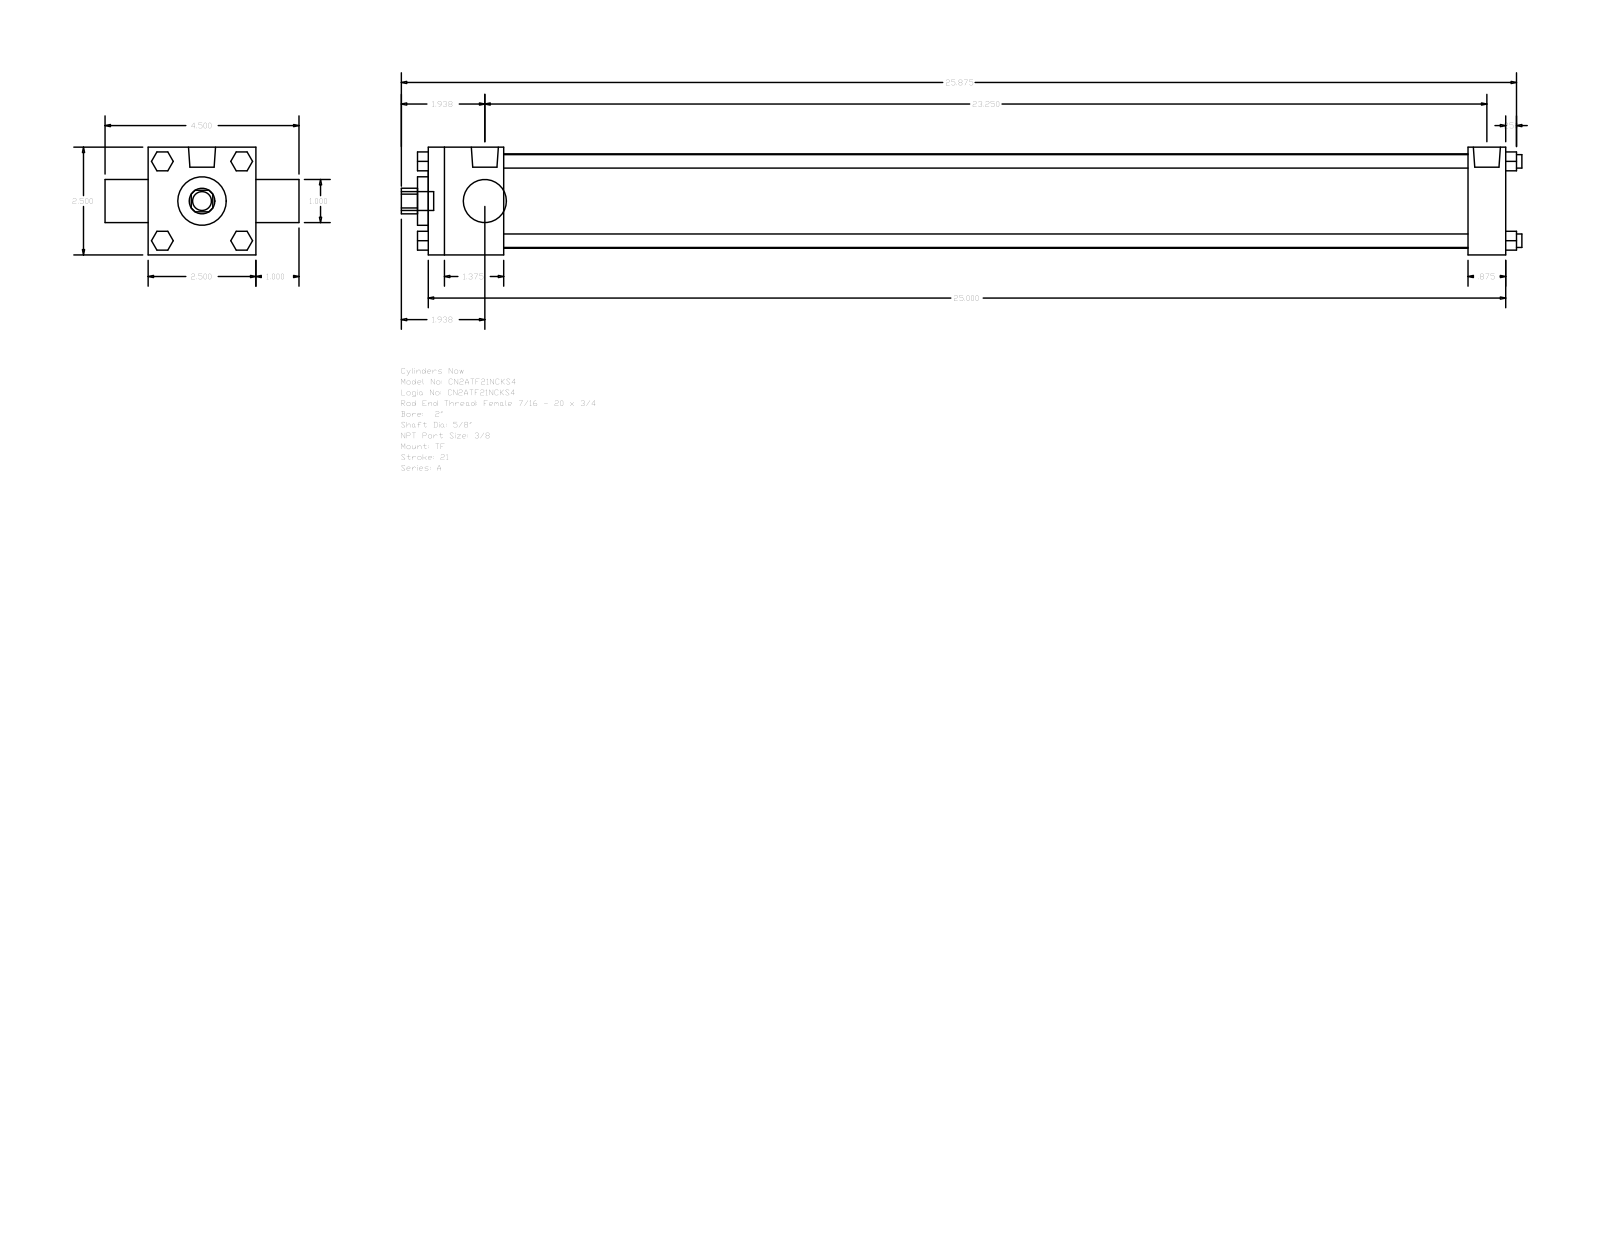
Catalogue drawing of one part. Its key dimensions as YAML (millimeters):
part_name: "A_TF__0200_0.625"
step_written_by: "GSSL Pune (CONFIG_CONTROL_DESIGN)"
units: millimeters
bodies: {solids: 0, faces: 120, planar: 92, cylindrical: 28, other: 0}
overall_size: [660.4, 114.3, 63.5]
round_holes:
  - {diameter: 15.88, count: 1}
  - {diameter: 25.4, count: 1}
  - {diameter: 28.57, count: 1}
  - {diameter: 55.63, count: 1}
round_bosses_or_shafts:
  - {diameter: 7.94, count: 4}
  - {diameter: 5.56, count: 3}
  - {diameter: 15.93, count: 2}
  - {diameter: 11.11, count: 1}
partial_cylinders:
  - {radius: 7.54, count: 1}
face_to_face_distances: [63.5, 635, 44.45, 612.77, 568.32, 590.55, 22.23, 25.4, 88.9, 641.35]
